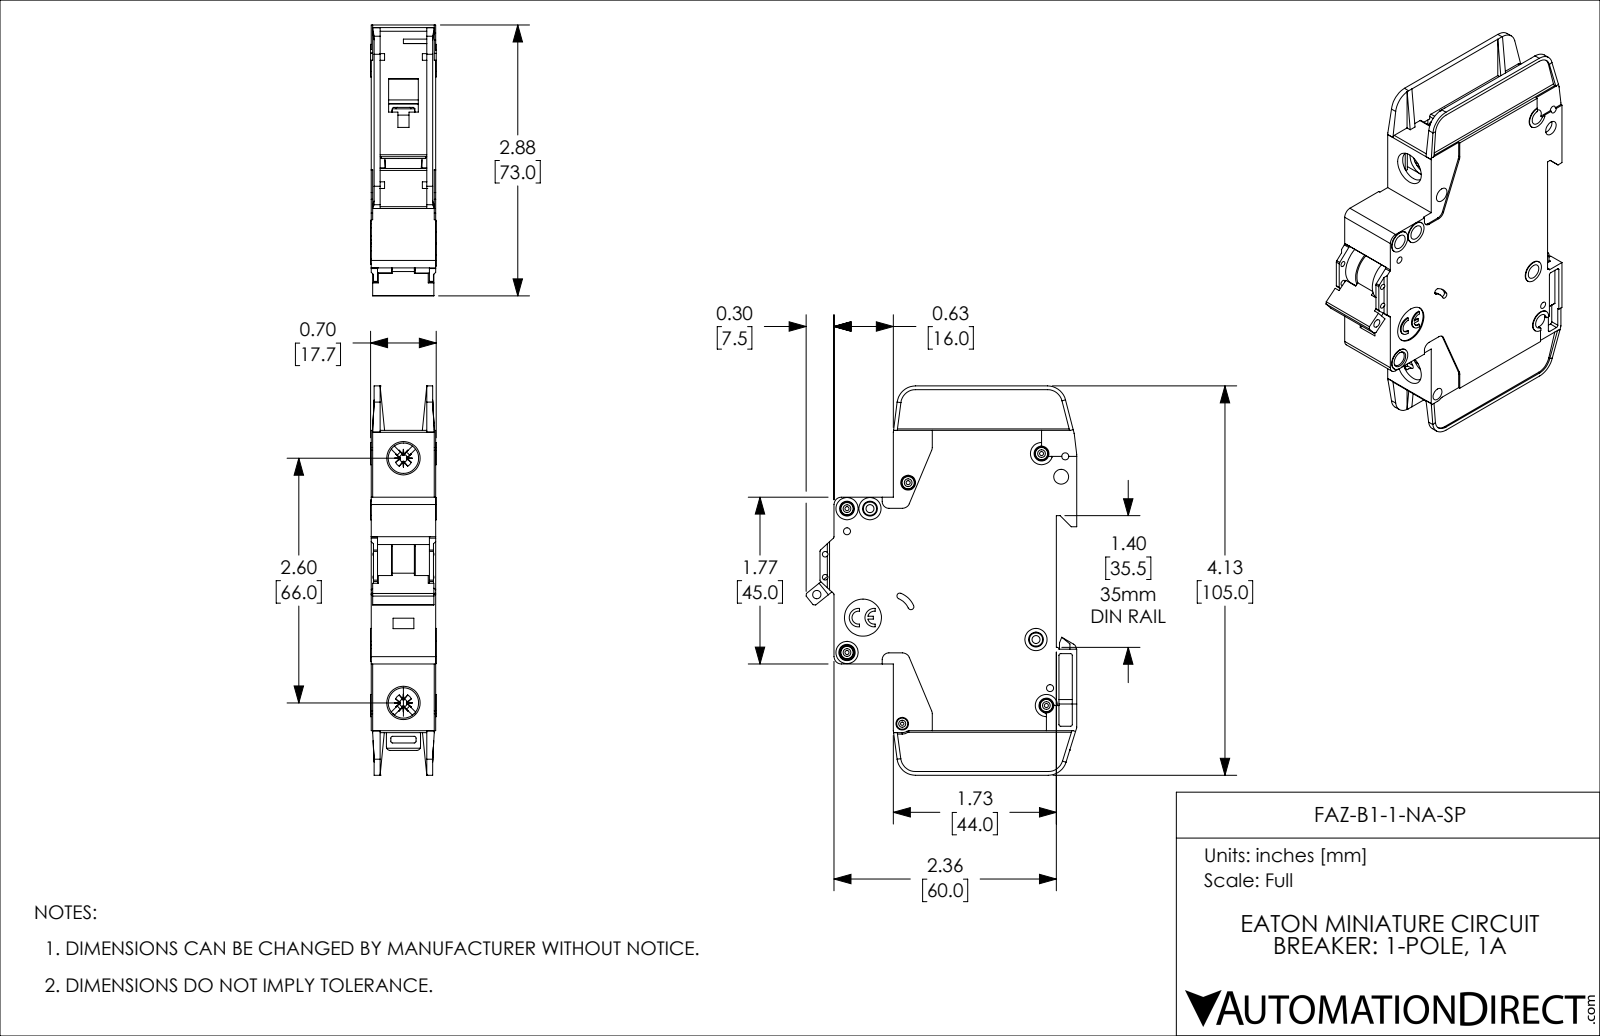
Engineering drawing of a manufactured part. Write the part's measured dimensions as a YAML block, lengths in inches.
part_name: "FAZ-B1-1-NA-SP"
step_written_by: "SolidWorks 2019 (AUTOMOTIVE_DESIGN)"
units: inches
bodies: {solids: 1, faces: 1127, planar: 671, cylindrical: 357, other: 99}
overall_size: [4.134, 2.876, 0.697]
volume: 4.682
surface_area: 41.01
round_holes:
  - {diameter: 0.157, count: 8}
  - {diameter: 0.043, count: 5}
  - {diameter: 0.075, count: 4}
  - {diameter: 0.059, count: 2}
  - {diameter: 0.085, count: 2}
  - {diameter: 0.323, count: 2}
  - {diameter: 0.035, count: 1}
  - {diameter: 0.089, count: 1}
  - {diameter: 0.098, count: 1}
  - {diameter: 0.134, count: 1}
  - {diameter: 0.394, count: 1}
round_bosses_or_shafts:
  - {diameter: 0.13, count: 5}
  - {diameter: 0.236, count: 4}
  - {diameter: 0.118, count: 2}
  - {diameter: 0.098, count: 1}
partial_cylinders:
  - {radius: 0.02, count: 42}
  - {radius: 0.016, count: 10}
  - {radius: 0.039, count: 10}
  - {radius: 0.079, count: 8}
  - {radius: 0.197, count: 5}
  - {radius: 0.008, count: 4}
  - {radius: 0.026, count: 4}
  - {radius: 0.043, count: 4}
face_to_face_distances: [0.047, 0.685, 0.591, 0.638, 0.094, 0.543, 0.016, 0.031, 0.496, 0.575]
hole_center_spacings: [0.244, 0.537, 0.87, 0.189, 0.199, 0.204, 0.221, 0.24]
